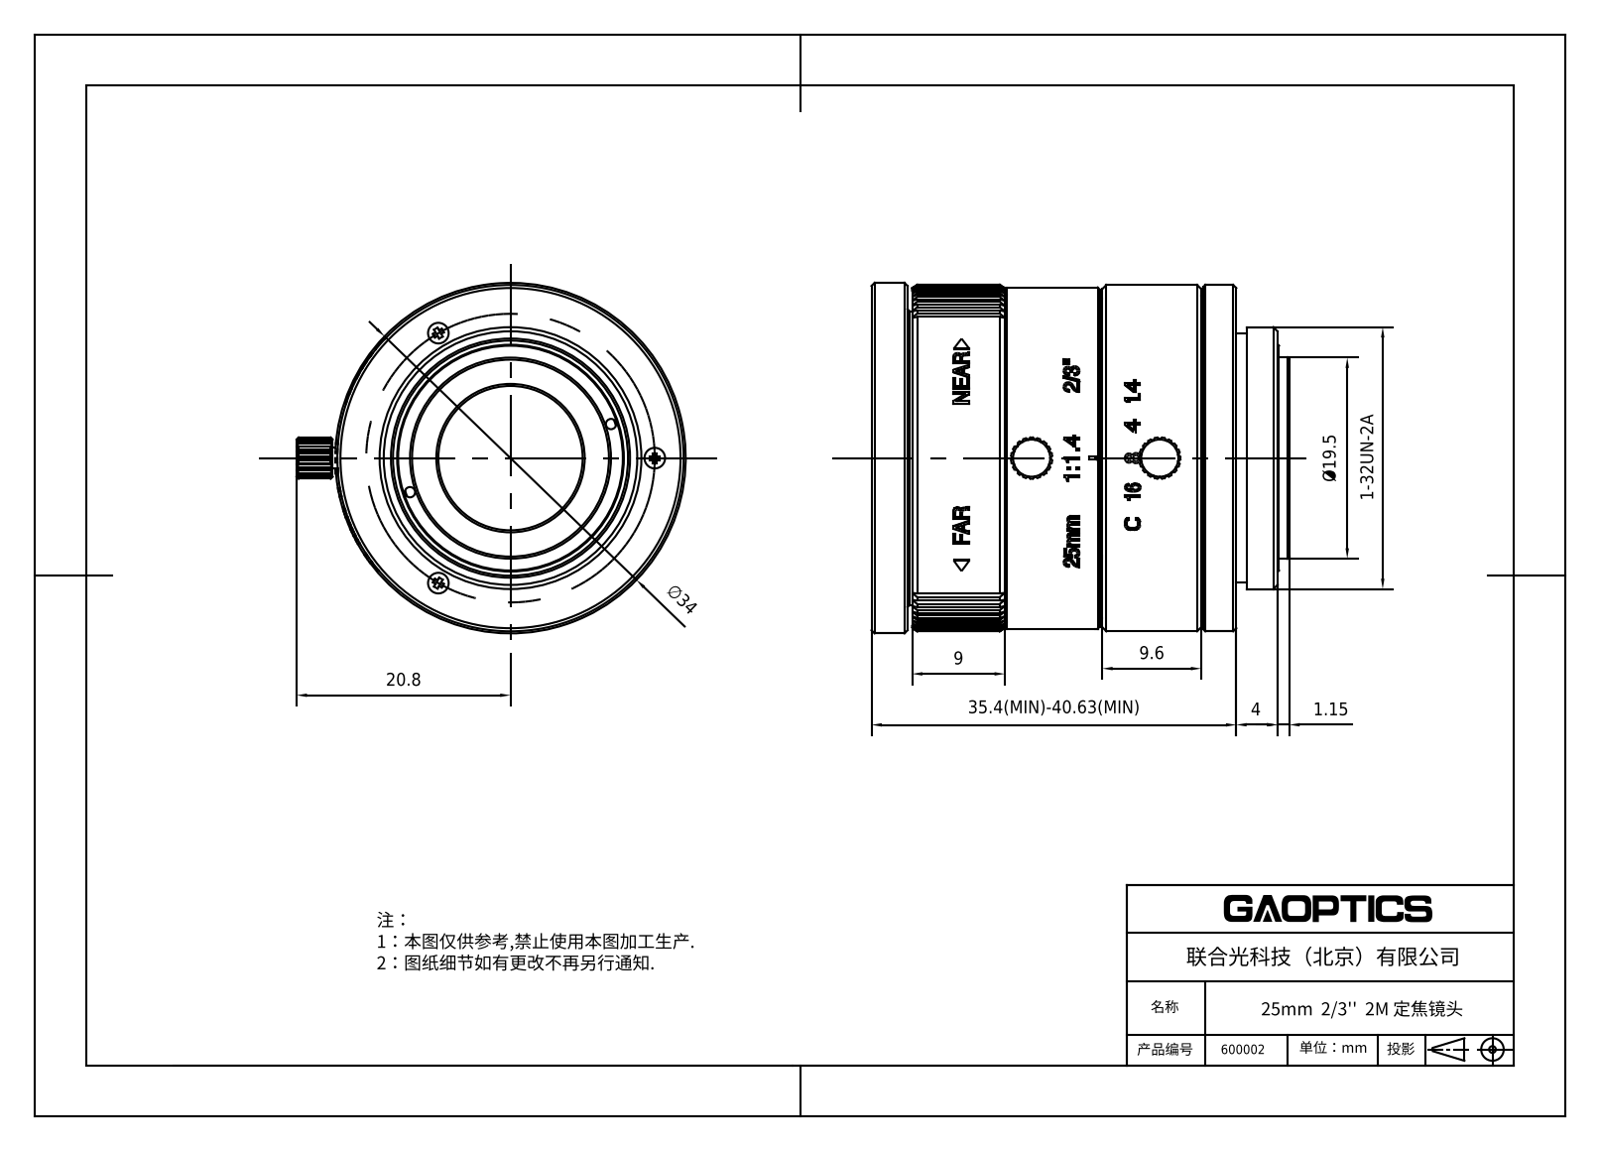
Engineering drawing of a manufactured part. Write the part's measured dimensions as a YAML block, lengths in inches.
part_name: "600002"
step_written_by: "SolidWorks 2020 (CONFIG_CONTROL_DESIGN)"
units: inches
bodies: {solids: 0, faces: 1306, planar: 579, cylindrical: 299, other: 428}
overall_size: [1.596, 1.486, 1.339]
round_holes:
  - {diameter: 0.079, count: 4}
  - {diameter: 0.071, count: 3}
  - {diameter: 0.063, count: 2}
  - {diameter: 0.043, count: 1}
  - {diameter: 0.551, count: 1}
  - {diameter: 0.638, count: 1}
  - {diameter: 0.685, count: 1}
  - {diameter: 0.787, count: 1}
  - {diameter: 0.803, count: 1}
  - {diameter: 0.819, count: 1}
  - {diameter: 0.835, count: 1}
  - {diameter: 0.85, count: 1}
round_bosses_or_shafts:
  - {diameter: 1.339, count: 1}
  - {diameter: 1.323, count: 1}
  - {diameter: 1.303, count: 1}
  - {diameter: 1.244, count: 1}
  - {diameter: 1.2, count: 1}
  - {diameter: 1.122, count: 1}
  - {diameter: 1.063, count: 1}
  - {diameter: 1, count: 1}
partial_cylinders:
  - {radius: 0.02, count: 6}
  - {radius: 0.049, count: 3}
  - {radius: 0.047, count: 1}
  - {radius: 0.059, count: 1}
  - {radius: 0.079, count: 1}
  - {radius: 0.616, count: 1}
  - {radius: 0.654, count: 1}
  - {radius: 0.655, count: 1}
face_to_face_distances: [0.016, 0.019, 1.246, 1.265, 1.23, 1.249, 0.138, 0.039, 1.419, 0.126]
hole_center_spacings: [0.551, 0.955, 0.954]
